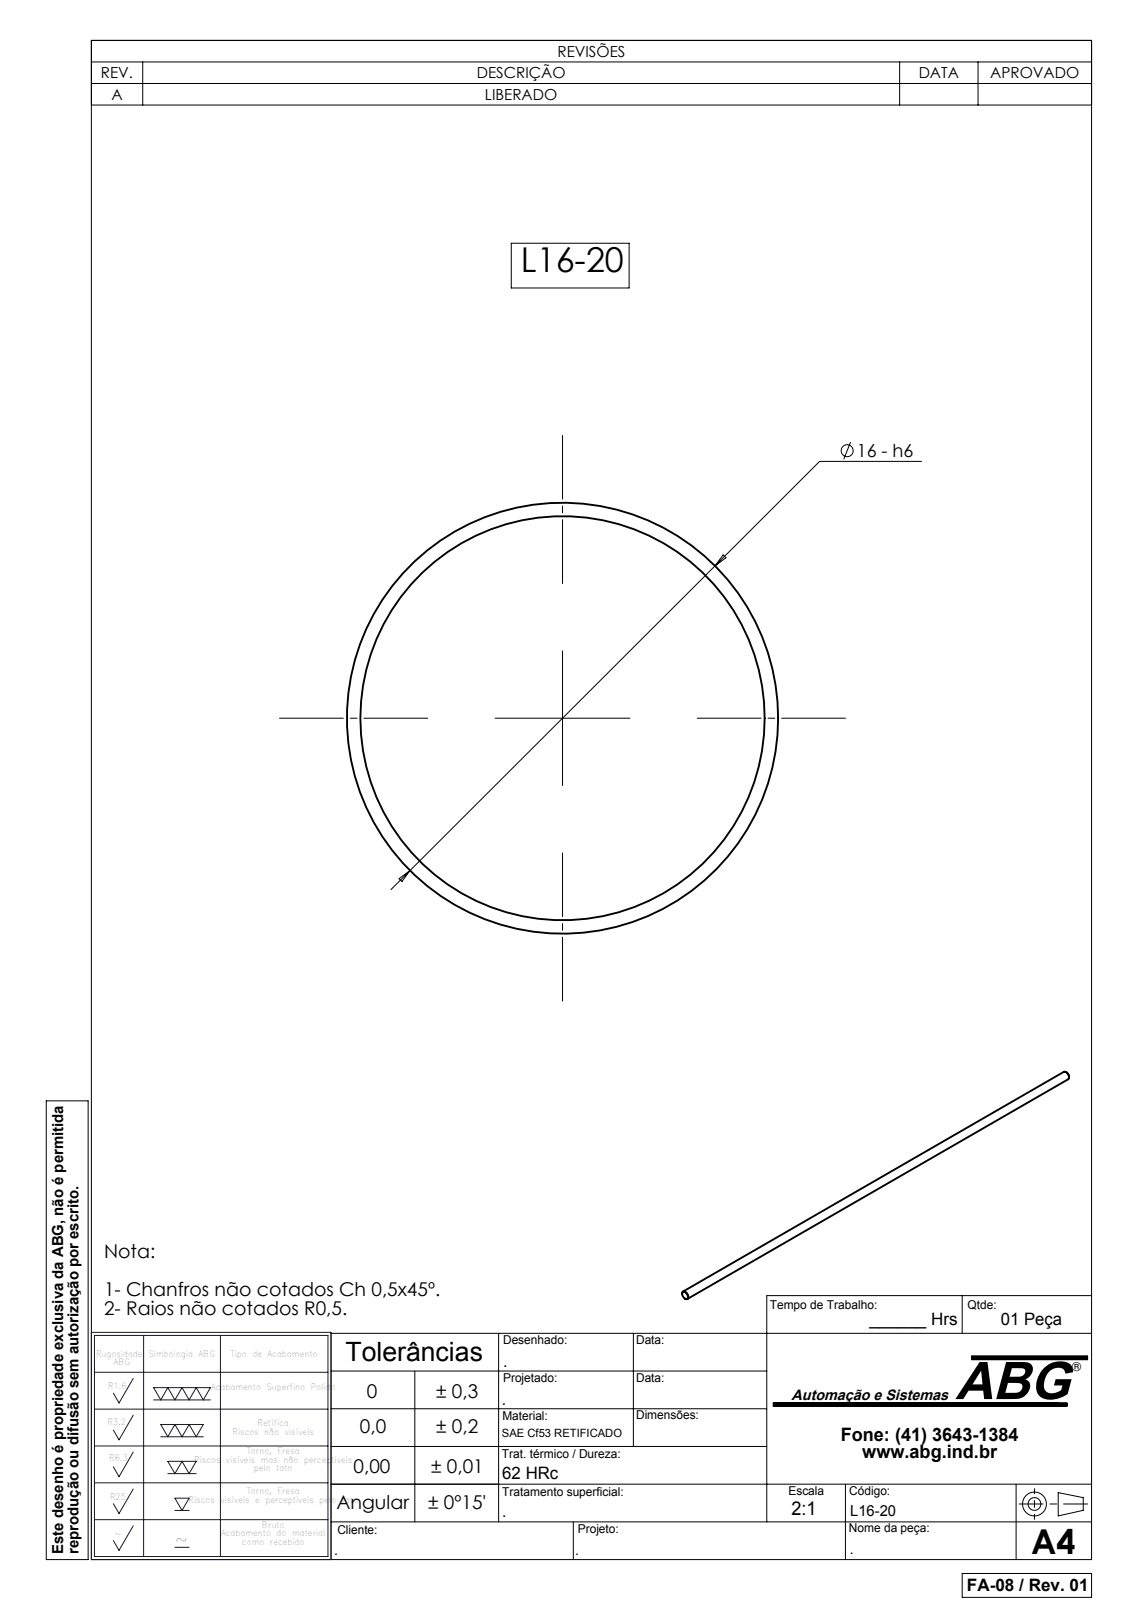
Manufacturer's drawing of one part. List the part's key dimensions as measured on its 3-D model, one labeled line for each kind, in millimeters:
Part name (STEP PRODUCT): L16-20
STEP written by: SolidWorks 2007 (CONFIG_CONTROL_DESIGN)
Units: millimetres
Bodies: 1 solid, 8 faces (2 planar, 2 cylindrical, 4 other)
Overall size (bounding box): 1000 × 16 × 16
Volume: 201 050 mm³ · Surface area: 50 638 mm²
Round bosses / shafts (diameter × count): ⌀16 ×1
Main face-to-face distances: 1000
